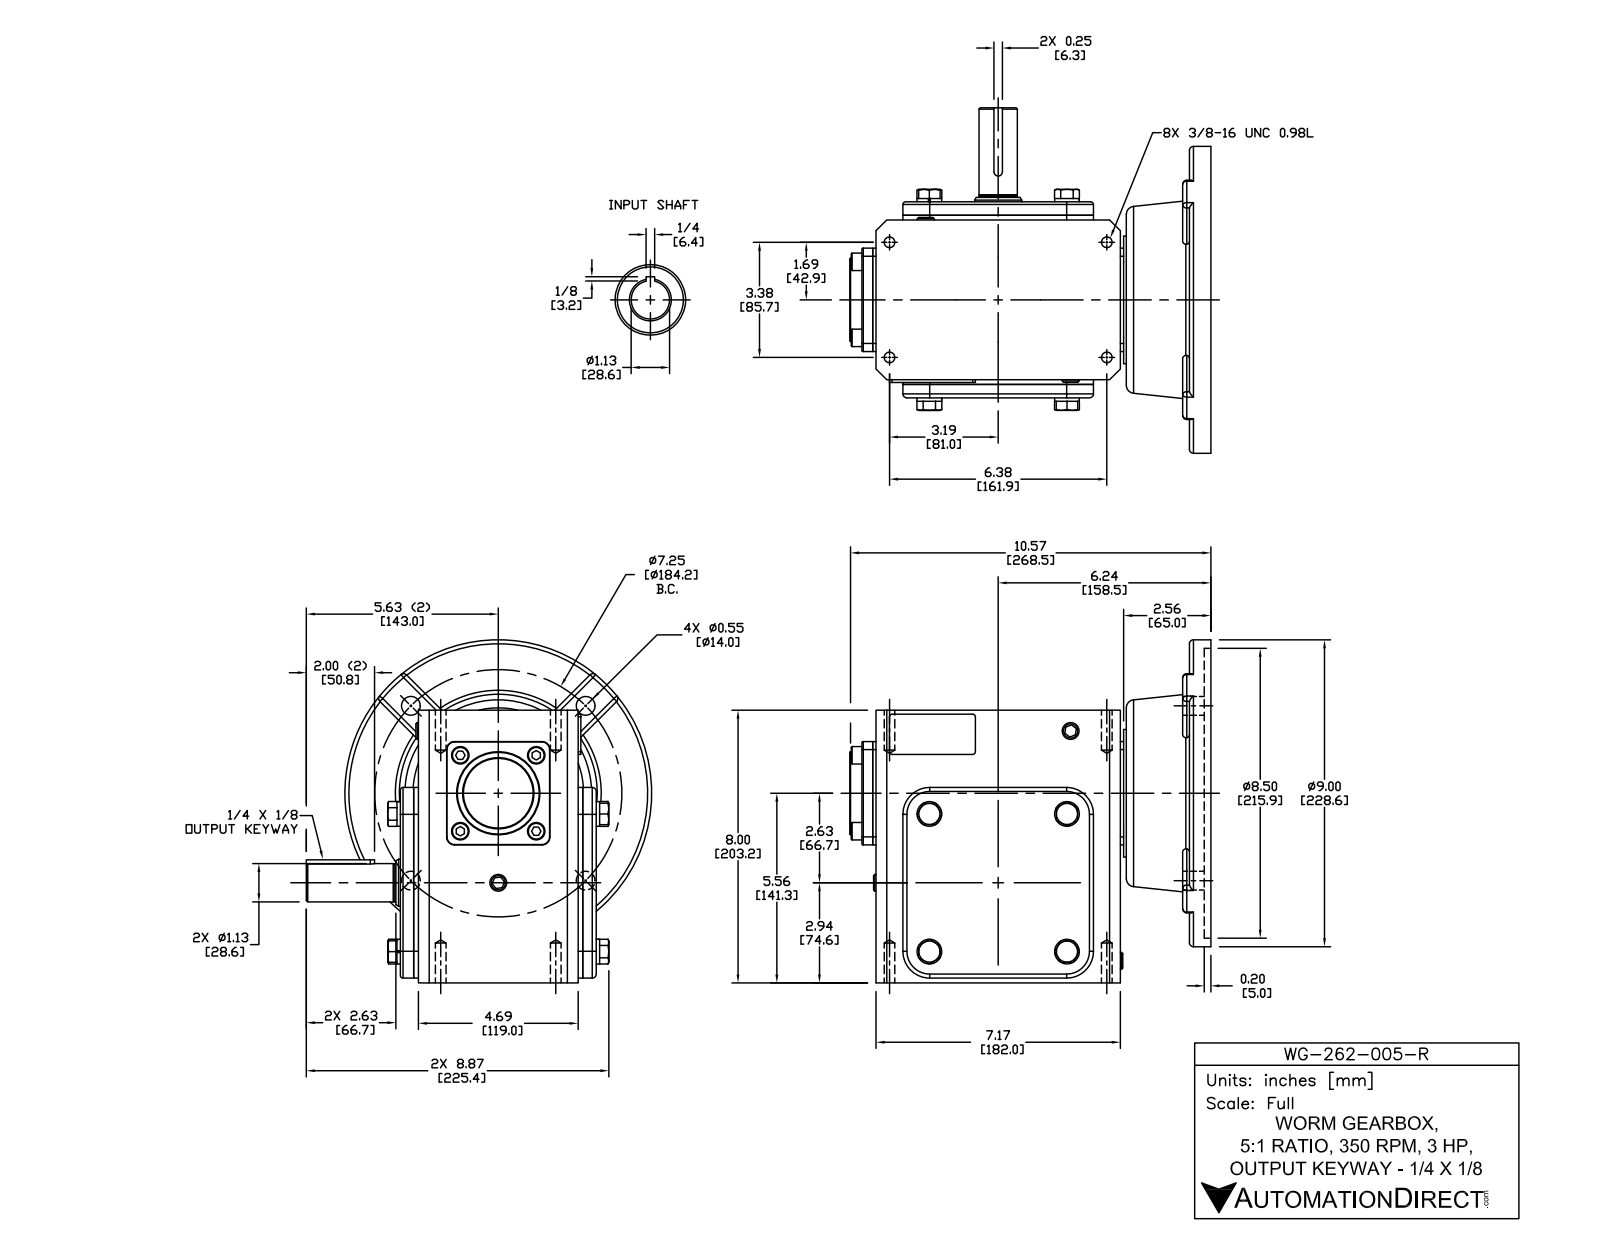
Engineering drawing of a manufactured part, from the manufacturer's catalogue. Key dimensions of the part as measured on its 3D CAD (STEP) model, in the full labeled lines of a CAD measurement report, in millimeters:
Part name (STEP PRODUCT): WG-262-005-R
STEP written by: SolidWorks 2015 (CONFIG_CONTROL_DESIGN)
Units: millimetres
Bodies: 31 solids, 552 faces (299 planar, 136 cylindrical, 117 other)
Overall size (bounding box): 269 × 257.3 × 255.6
Volume: 5 398 000 mm³ · Surface area: 484 500 mm²
Round holes (diameter × count): ⌀8 ×4, ⌀14 ×4, ⌀15 ×1, ⌀28.6 ×1, ⌀35 ×1, ⌀50 ×1, ⌀52 ×1, ⌀97 ×1, ⌀215.9 ×1
Round bosses / shafts (diameter × count): ⌀18.4 ×4, ⌀13 ×4, ⌀228.6 ×1, ⌀62 ×1, ⌀45 ×1, ⌀29 ×1, ⌀28.6 ×1, ⌀28.3 ×1
Partial cylindrical surfaces — rounded edges, fillets, slot ends (radius × count): R3 ×15, R2 ×11, R6 ×4, R20 ×4, R0.5 ×2, R1 ×2, R3.2 ×1
Main face-to-face distances: 126, 10, 136, 13.5, 132.5, 3.5, 122.5, 203.2, 11, 146
Hole centre spacings: 92.1, 130.2, 65.1, 85.7, 147, 161.9, 183.2, 184.2
